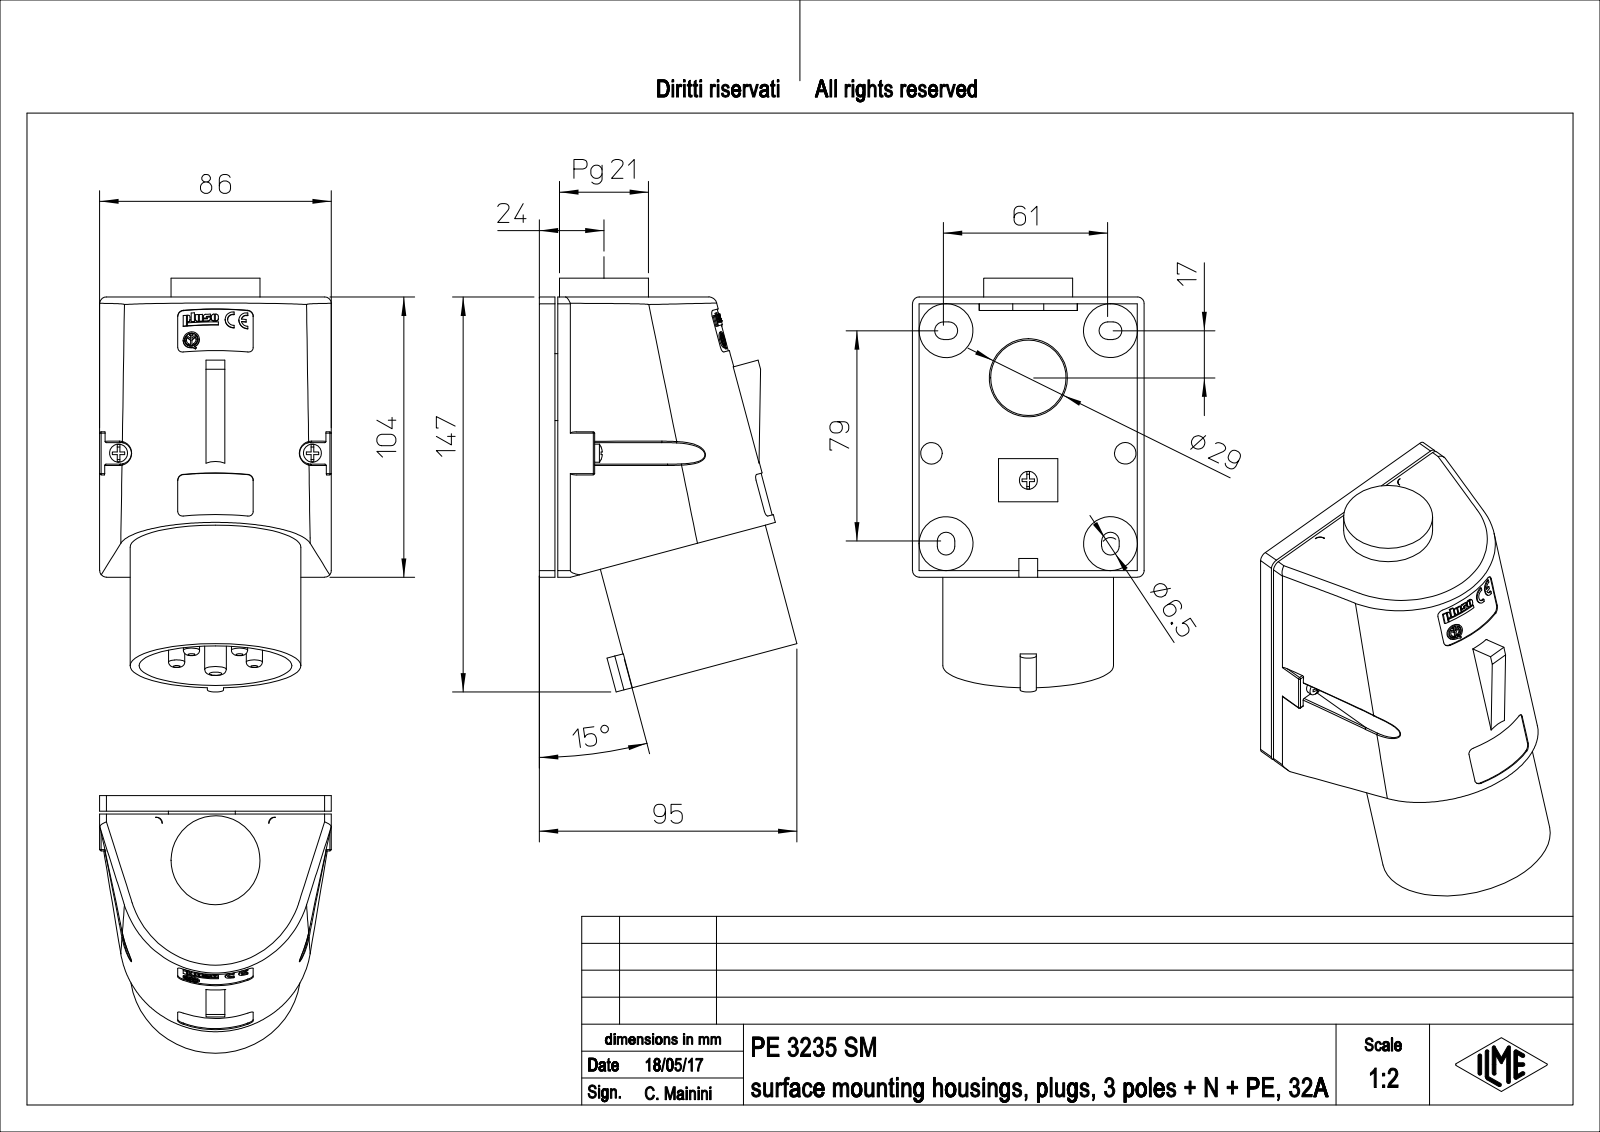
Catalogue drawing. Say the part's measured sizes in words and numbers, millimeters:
The part is named "PE_3235_SM". Its 3-D file was written by "PTC Creo Elements/Direct Modeling 19.0E 27-Jun-2016 (C) Parametric Technology GmbH (AUTOMOTIVE_DESIGN)". It is 1 solid with 1055 faces: 668 planar, 220 cylindrical and 167 other. Overall it measures 153.55 by 95.62 by 86 millimeters. Its volume is 518 948 cubic millimeters and its surface area 96 274 square millimeters. Round holes: 4 of diameter 6.1, 2 of diameter 2.8, 2 of diameter 3.2, 2 of diameter 4, 2 of diameter 4.5, 1 of diameter 4.2, 1 of diameter 5.04, 1 of diameter 27.54, 1 of diameter 29, 1 of diameter 32, 1 of diameter 56.7. Round bosses or shafts: 5 of diameter 6.7, 5 of diameter 6, 4 of diameter 20, 3 of diameter 8, 2 of diameter 3, 1 of diameter 63.4, 1 of diameter 33, 1 of diameter 24.84. Partial cylindrical surfaces (rounded edges, fillets, slot ends): 20 of radius 0.5, 11 of radius 0.17, 10 of radius 2, 9 of radius 0.86, 8 of radius 3.25, 6 of radius 2.5, 4 of radius 0.75, 4 of radius 4.5. The main face-to-face distances are 1.07, 4.75, 5.82, 7, 1, 5.75, 6.82, 2.25, 2.5, 8. The hole center spacings are 15.15, 72, 17.81, 21.93, 24.8, 28.81, 37.36, 37.37.
